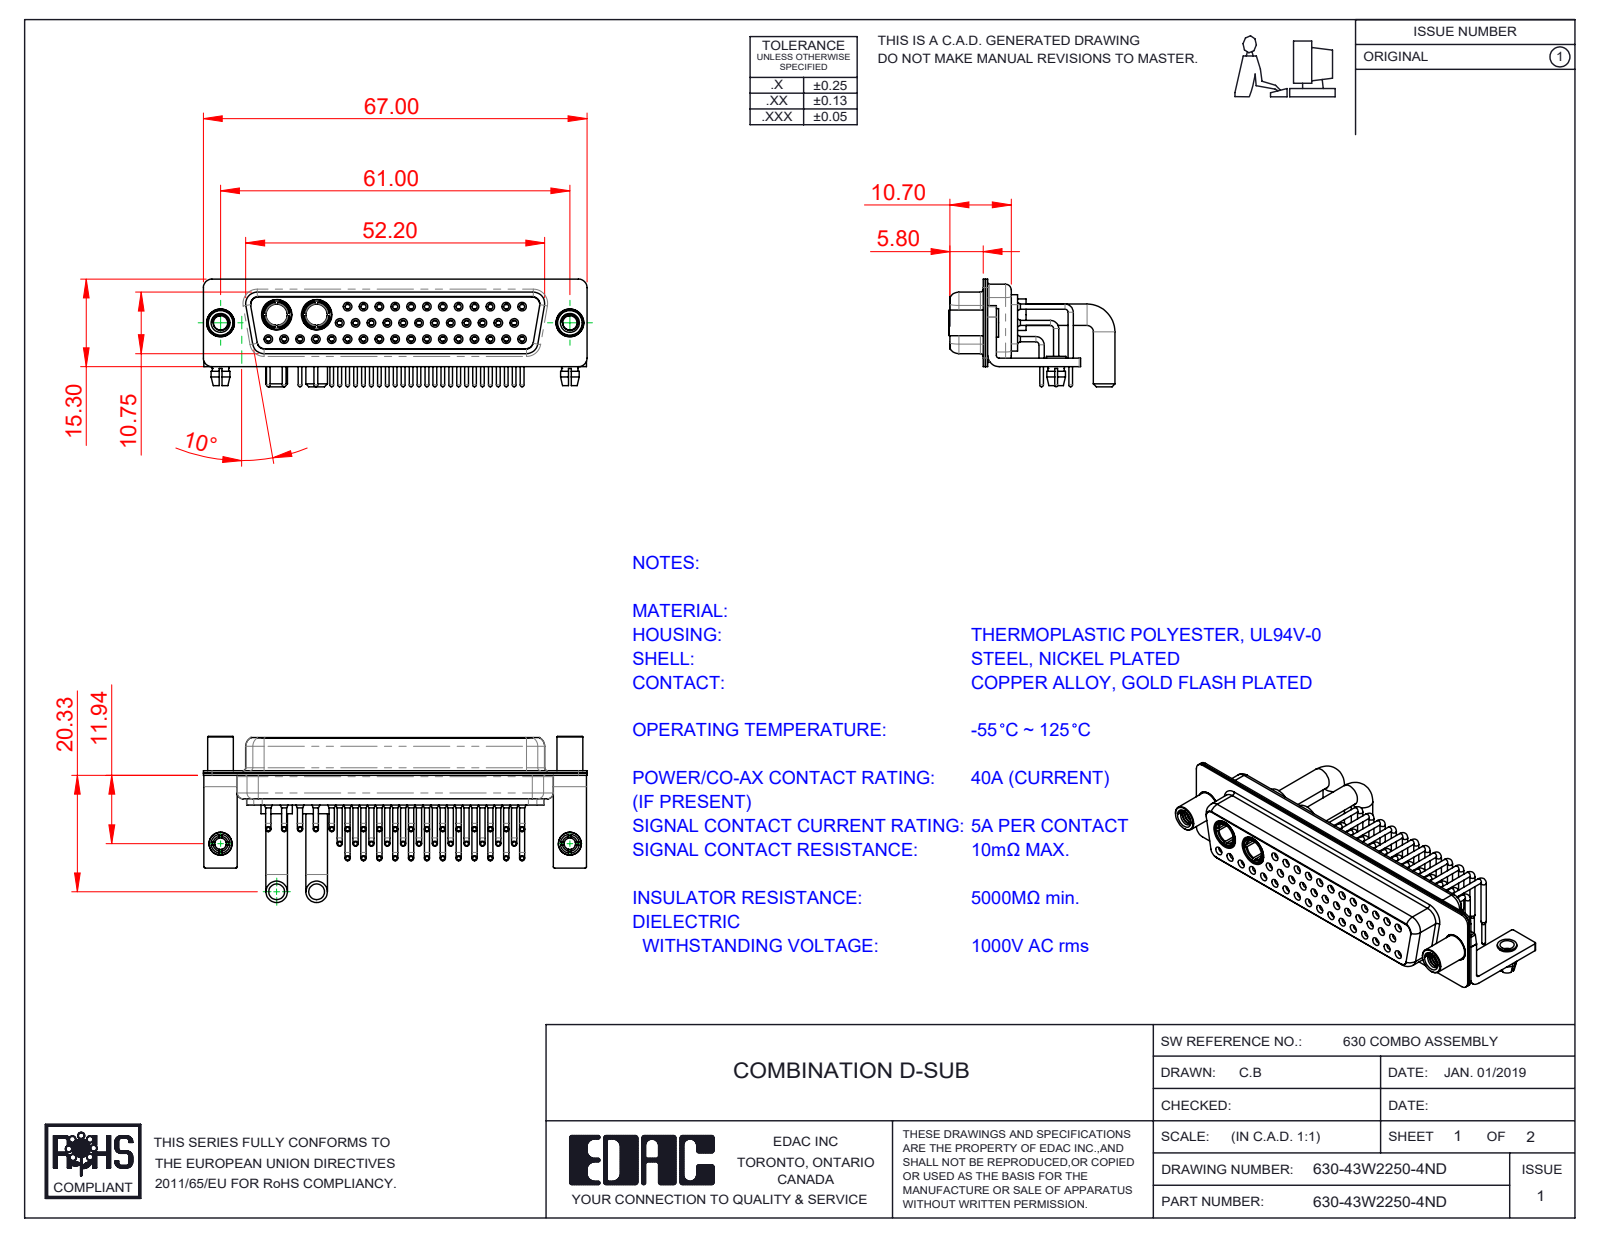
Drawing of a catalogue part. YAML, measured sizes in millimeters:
part_name: "630Combo Contact Row 1_50 Contacts; 630Combo Contact Row 2_50 Contacts; 630Combo Housing_43W2; Power Socket_Ext 40A RA 50 (+7 more)"
step_written_by: "SolidWorks 2020 (CONFIG_CONTROL_DESIGN)"
units: millimeters
bodies: {solids: 54, faces: 2798, planar: 810, cylindrical: 1234, other: 754}
overall_size: [67, 29, 18.8]
volume: 8050
surface_area: 17385
round_holes:
  - {diameter: 2, count: 43}
  - {diameter: 0.9, count: 41}
  - {diameter: 1.1, count: 41}
  - {diameter: 1.5, count: 41}
  - {diameter: 1.6, count: 29}
  - {diameter: 1.7, count: 12}
  - {diameter: 2.5, count: 4}
  - {diameter: 4.85, count: 4}
  - {diameter: 3.2, count: 2}
  - {diameter: 3.7, count: 2}
  - {diameter: 4, count: 2}
  - {diameter: 4.05, count: 2}
round_bosses_or_shafts:
  - {diameter: 0.9, count: 41}
  - {diameter: 0.65, count: 41}
  - {diameter: 1.6, count: 12}
  - {diameter: 3.75, count: 4}
  - {diameter: 5.5, count: 2}
  - {diameter: 5.2, count: 2}
  - {diameter: 5, count: 2}
  - {diameter: 4.96, count: 2}
partial_cylinders:
  - {radius: 0.25, count: 16}
  - {radius: 1.5, count: 16}
  - {radius: 2, count: 13}
  - {radius: 1.35, count: 12}
  - {radius: 1.6, count: 8}
  - {radius: 0.5, count: 5}
  - {radius: 0.6, count: 4}
  - {radius: 0.65, count: 4}
face_to_face_distances: [0.4, 6, 1.5, 5.6, 0.8, 5.8, 5.2, 11.28, 1.82, 6.2]
hole_center_spacings: [2.77, 3.16, 5.54, 8.31, 11.08, 13.85, 16.62, 19.39]
